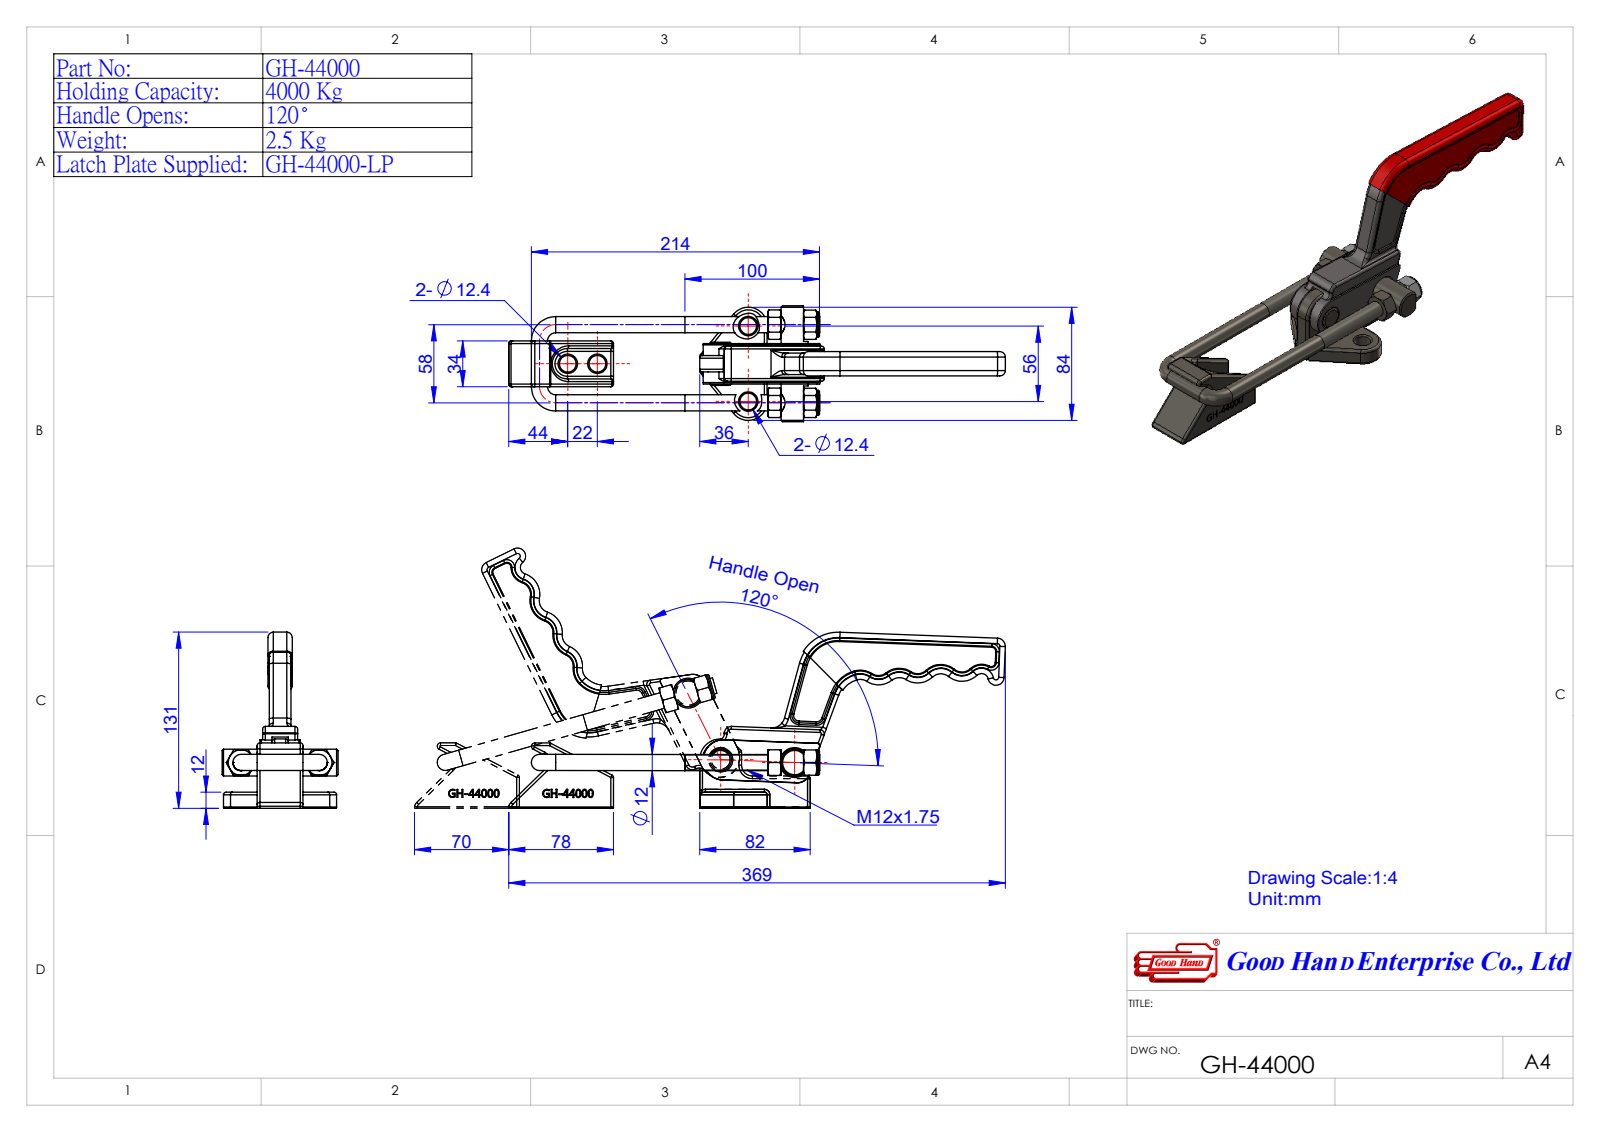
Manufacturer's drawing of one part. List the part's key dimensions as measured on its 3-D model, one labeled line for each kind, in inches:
Part name (STEP PRODUCT): Group5^GH-44000(簡化); GH-44000(簡化); 24400013-1^GH-44000(簡化); Group1^GH-44000(簡化) (+2 more)
STEP written by: SolidWorks 2016 (AUTOMOTIVE_DESIGN)
Units: inches
Bodies: 8 solids, 493 faces (114 planar, 165 cylindrical, 214 other)
Overall size (bounding box): 14.522 × 5.146 × 3.386
Volume: 21.26 in³ · Surface area: 149 in²
Round holes (diameter × count): ⌀0.472 ×4, ⌀0.488 ×4, ⌀0.402 ×2, ⌀0.5 ×2, ⌀0.165 ×1, ⌀0.787 ×1
Round bosses / shafts (diameter × count): ⌀0.472 ×3, ⌀0.728 ×2
Partial cylindrical surfaces — rounded edges, fillets, slot ends (radius × count): R0.079 ×51, R0.157 ×10, R0.118 ×9, R0.039 ×4, R0.197 ×3, R0.236 ×3, R0.354 ×3, R0.63 ×3
Main face-to-face distances: 0.075, 0.555, 0.079, 0.354, 0.984, 0.429, 0.909, 1.26, 0.906, 0.276
Hole centre spacings: 2.283, 4.545, 5.389, 0.866, 2.165, 2.205
